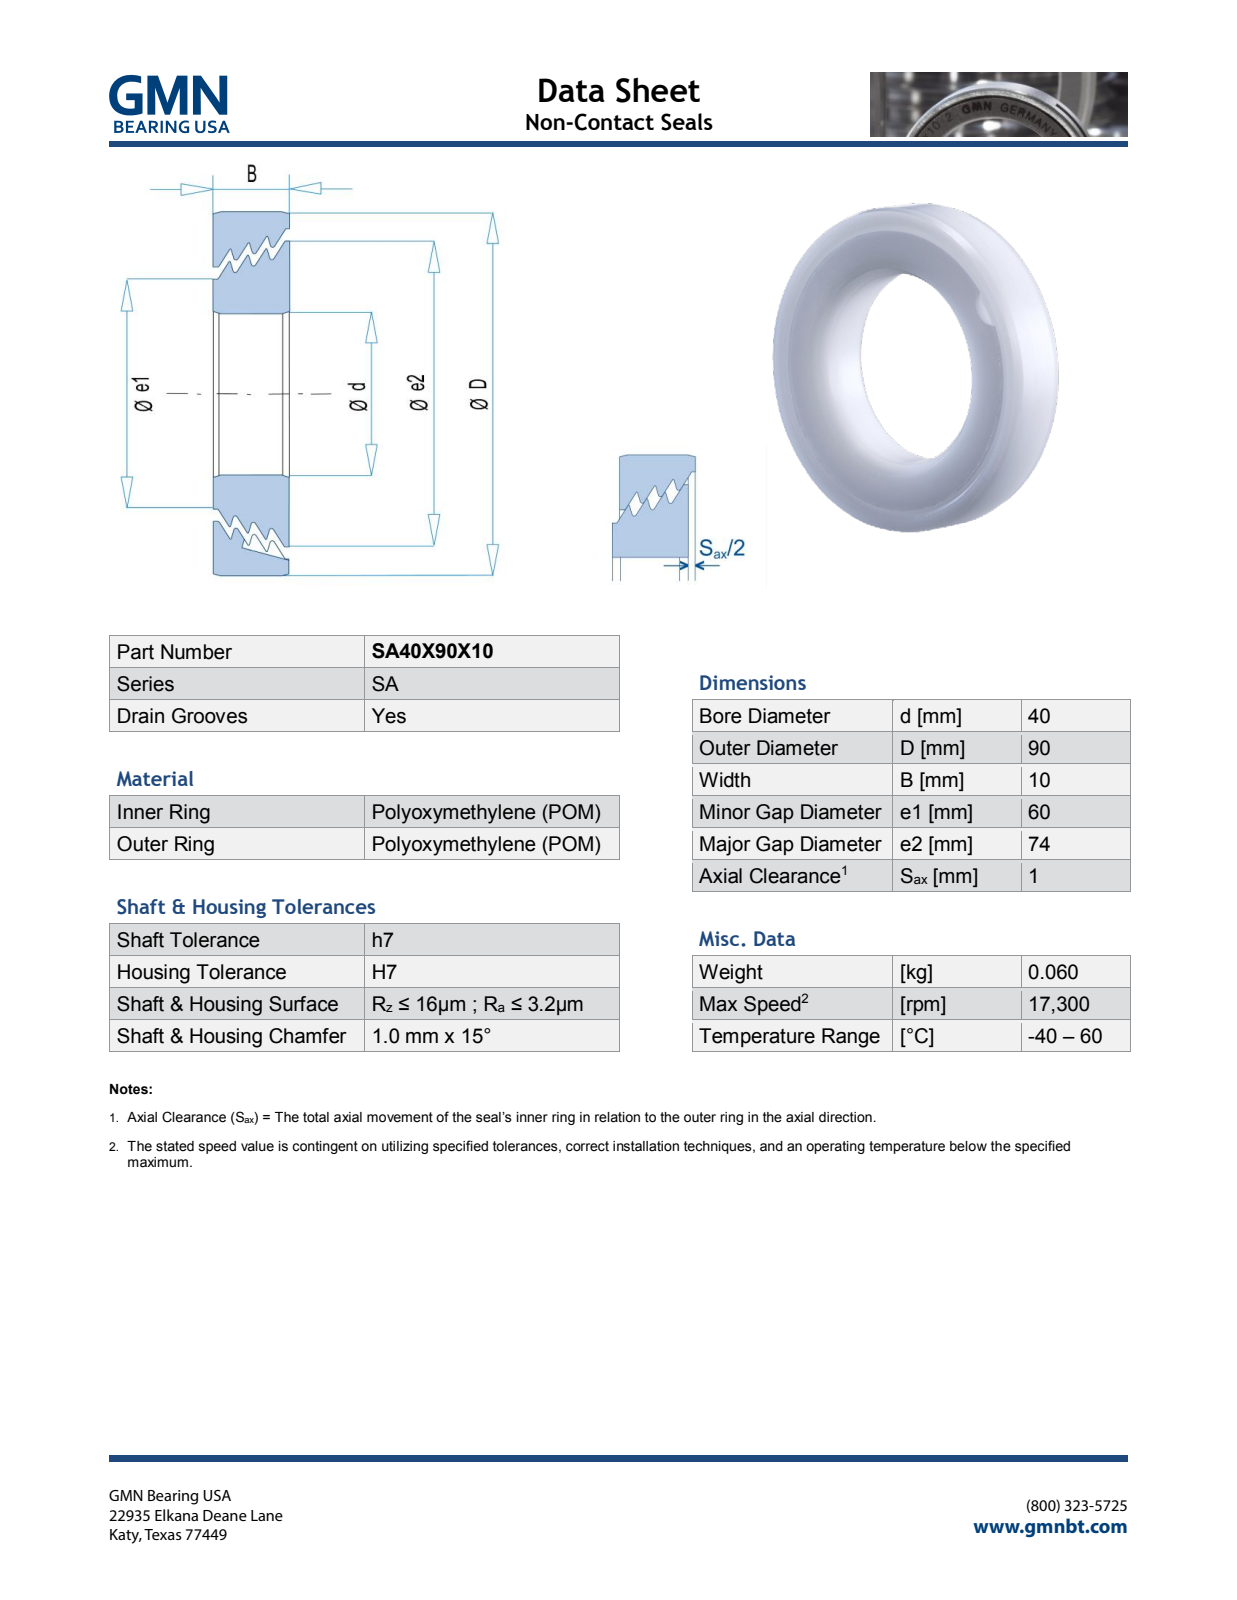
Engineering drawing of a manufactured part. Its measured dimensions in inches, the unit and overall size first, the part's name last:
Units: inches
Overall size (bounding box): 3.543 × 3.543 × 0.396
Round holes (diameter × count): ⌀1.575 ×1, ⌀2.426 ×1, ⌀2.978 ×1
Round bosses / shafts (diameter × count): ⌀3.543 ×1, ⌀2.913 ×1, ⌀2.362 ×1
Partial cylindrical surfaces — rounded edges, fillets, slot ends (radius × count): R0.236 ×1
Main face-to-face distances: 0.394, 0.396, 0.215, 0.212, 0.181, 0.024, 0.024, 0.19, 0.167, 0.024
Volume: 3 in³ · Surface area: 34.52 in²
Bodies: 2 solids, 670 faces (597 planar, 13 cylindrical, 60 other)
Part name (STEP PRODUCT): SA40X90X10_PRT
STEP written by: PRO/ENGINEER BY PARAMETRIC TECHNOLOGY CORPORATION, 2013150 (AUTOMOTIVE_DESIGN)
